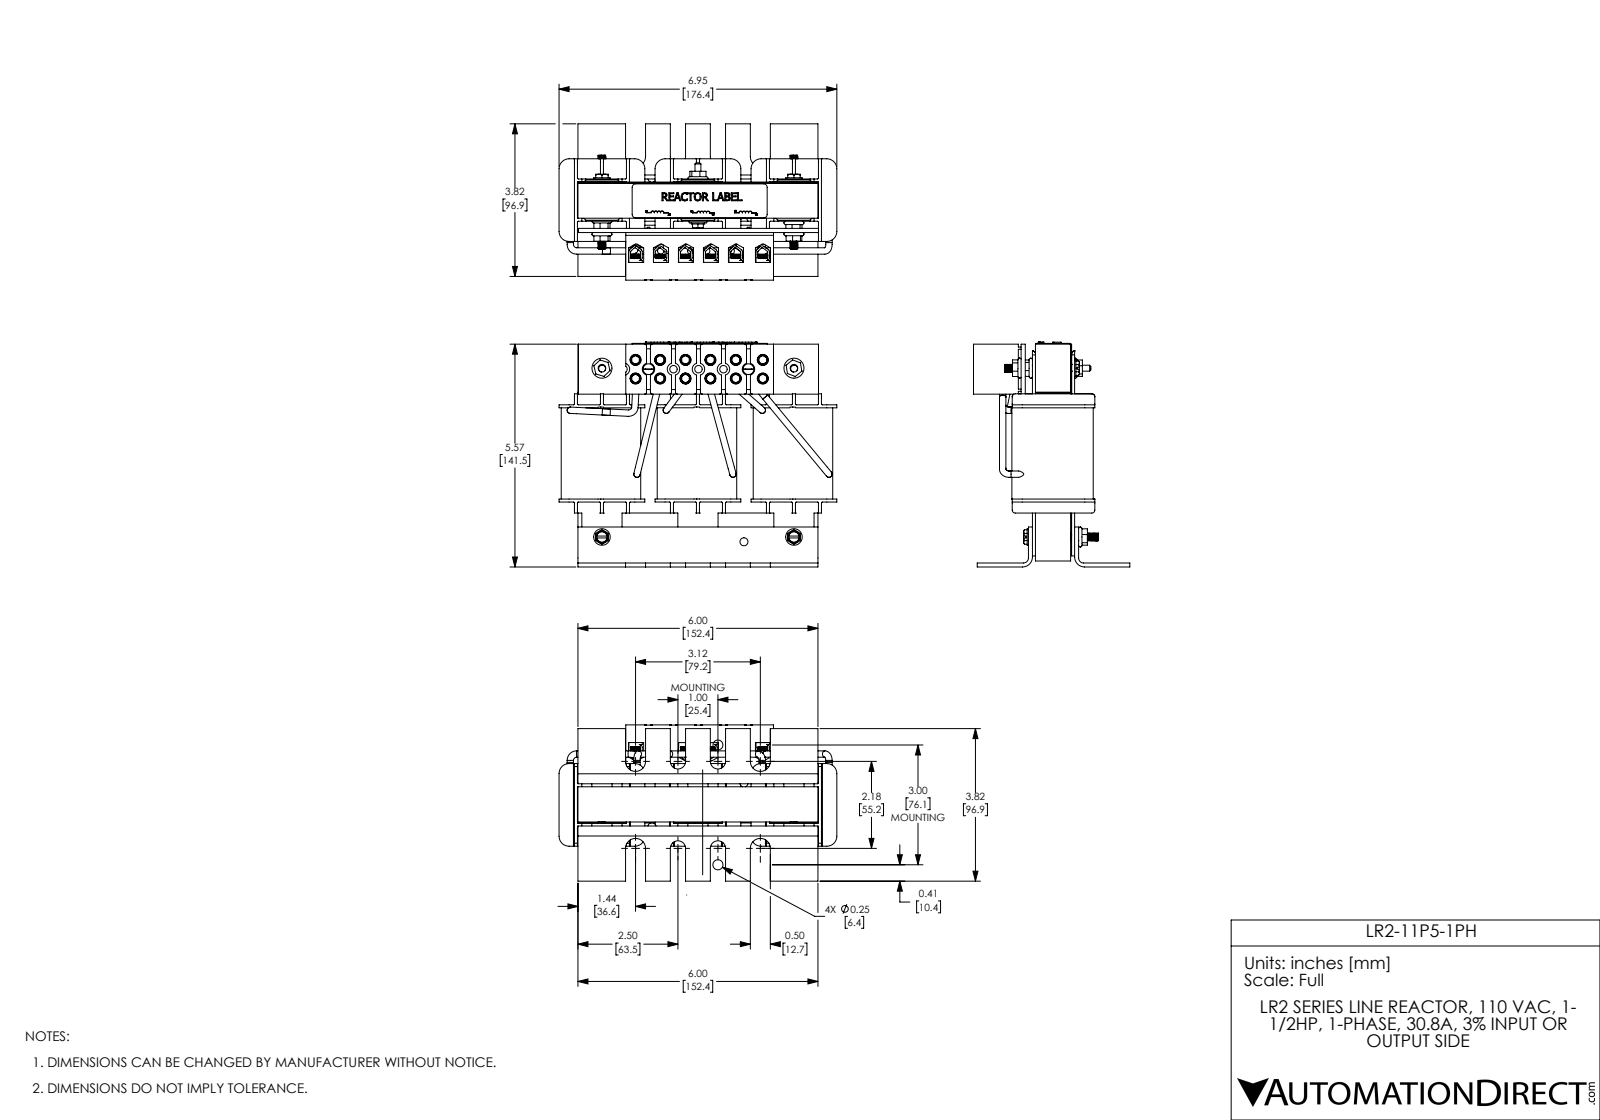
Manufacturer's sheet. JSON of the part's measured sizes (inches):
{"part_name": "D Frame r1", "step_written_by": "SolidWorks 2017 (AUTOMOTIVE_DESIGN)", "units": "inches", "bodies": {"solids": 55, "faces": 4717, "planar": 1597, "cylindrical": 2371, "other": 749}, "overall_size": [6.945, 5.62, 3.908], "volume_in3": 40.72, "surface_area_in2": 633.8, "round_holes": [[0.276, 16], [0.31, 7], [0.177, 6], [0.186, 5], [0.25, 5], [0.145, 4], [0.202, 3], [0.124, 2], [0.2, 2], [0.145, 1], [0.188, 1]], "round_bosses_or_shafts": [[0.159, 15], [0.26, 12], [0.25, 12], [0.204, 12], [0.159, 6], [0.5, 5], [0.414, 4], [0.19, 4]], "partial_cylinders_radius": [[0.038, 159], [0.025, 94], [0.25, 48], [0.01, 42], [0.029, 24], [0.05, 20], [0.076, 18], [0.039, 12]], "face_to_face_distances": [0.88, 2.4, 0.1, 0.075, 0.075, 4.8, 1.3, 1.055, 0.024, 0.904], "hole_center_spacings": [0.465, 1.257, 2.4, 1.25, 0.373, 0.378, 0.381, 0.386]}
